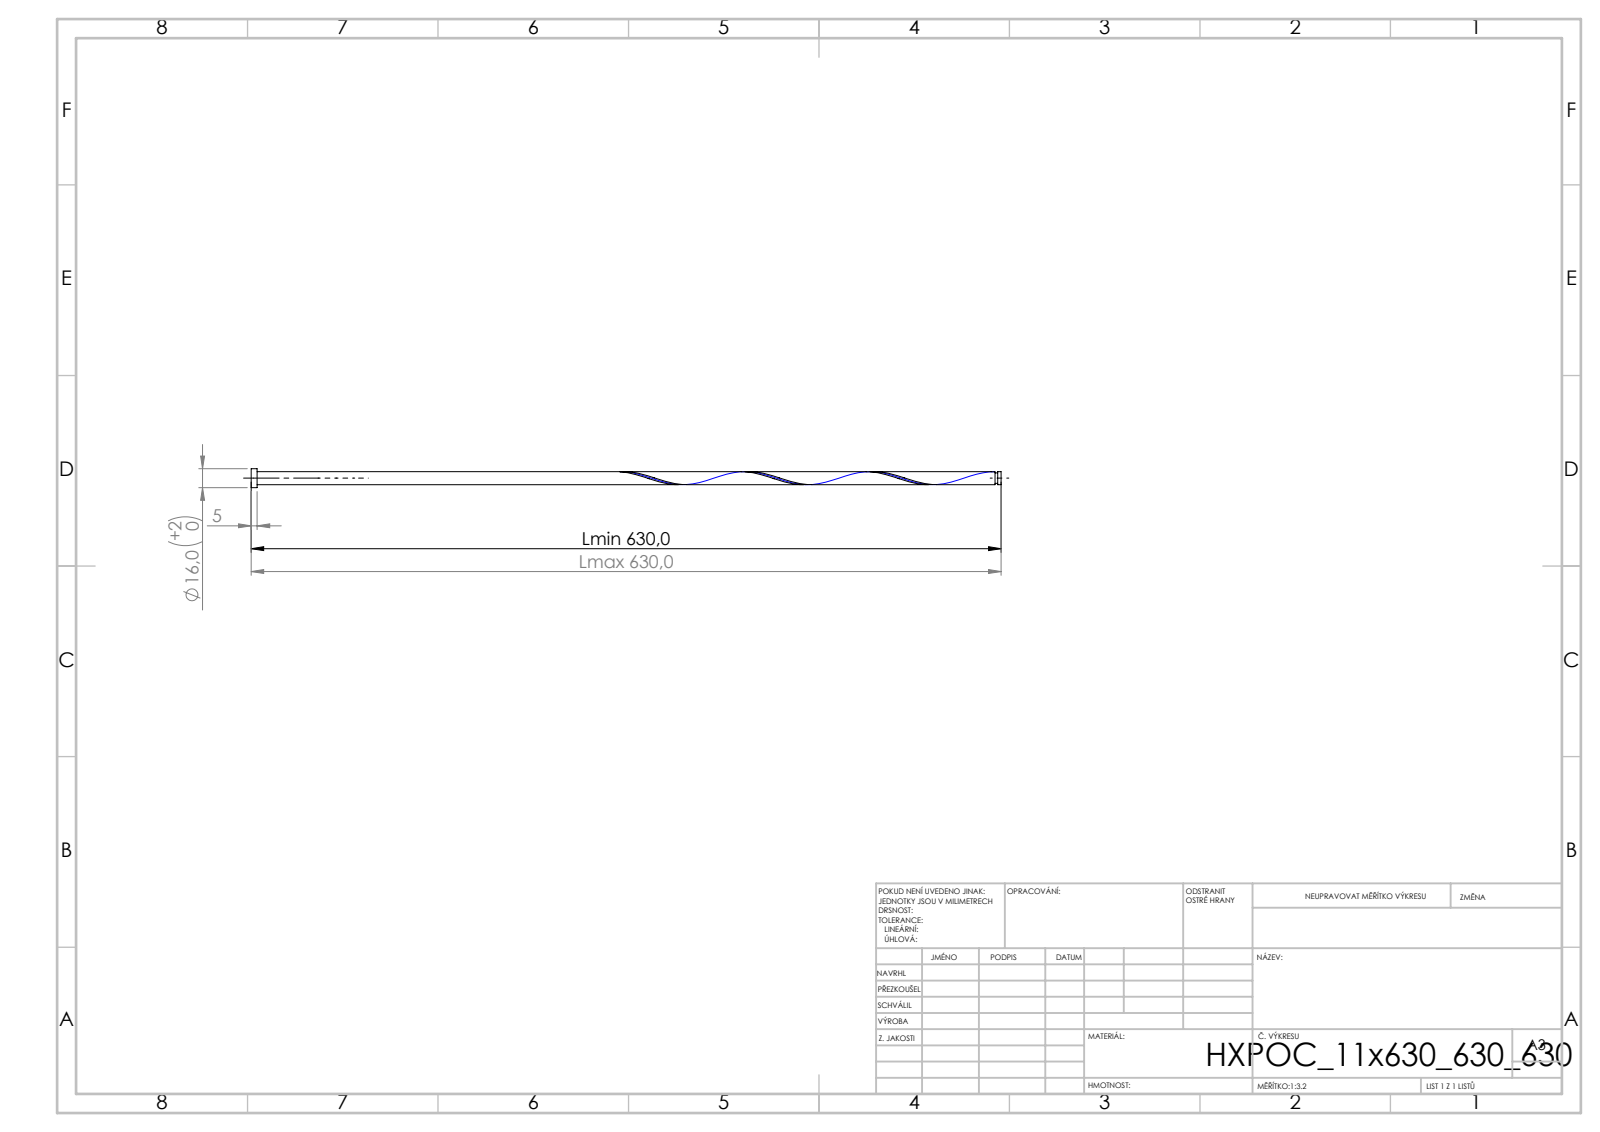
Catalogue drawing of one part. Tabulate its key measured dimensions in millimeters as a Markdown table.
| quantity | value |
| --- | --- |
| STEP written by | SolidWorks 2019 (CONFIG_CONTROL_DESIGN) |
| units | millimeters |
| bodies | 1 solid, 16 faces (6 planar, 9 cylindrical, 1 other) |
| overall size | 630 × 16 × 16 |
| volume | 73 056 mm³ |
| surface area | 29 912 mm² |
| round bosses / shafts (diameter × count) | 16 × 1, 11 × 1, 8.8 × 1 |
| main face-to-face distances | 5, 630, 625, 627.13, 622.13, 2.87, 624.93, 619.93, 2.2, 5.07 |
